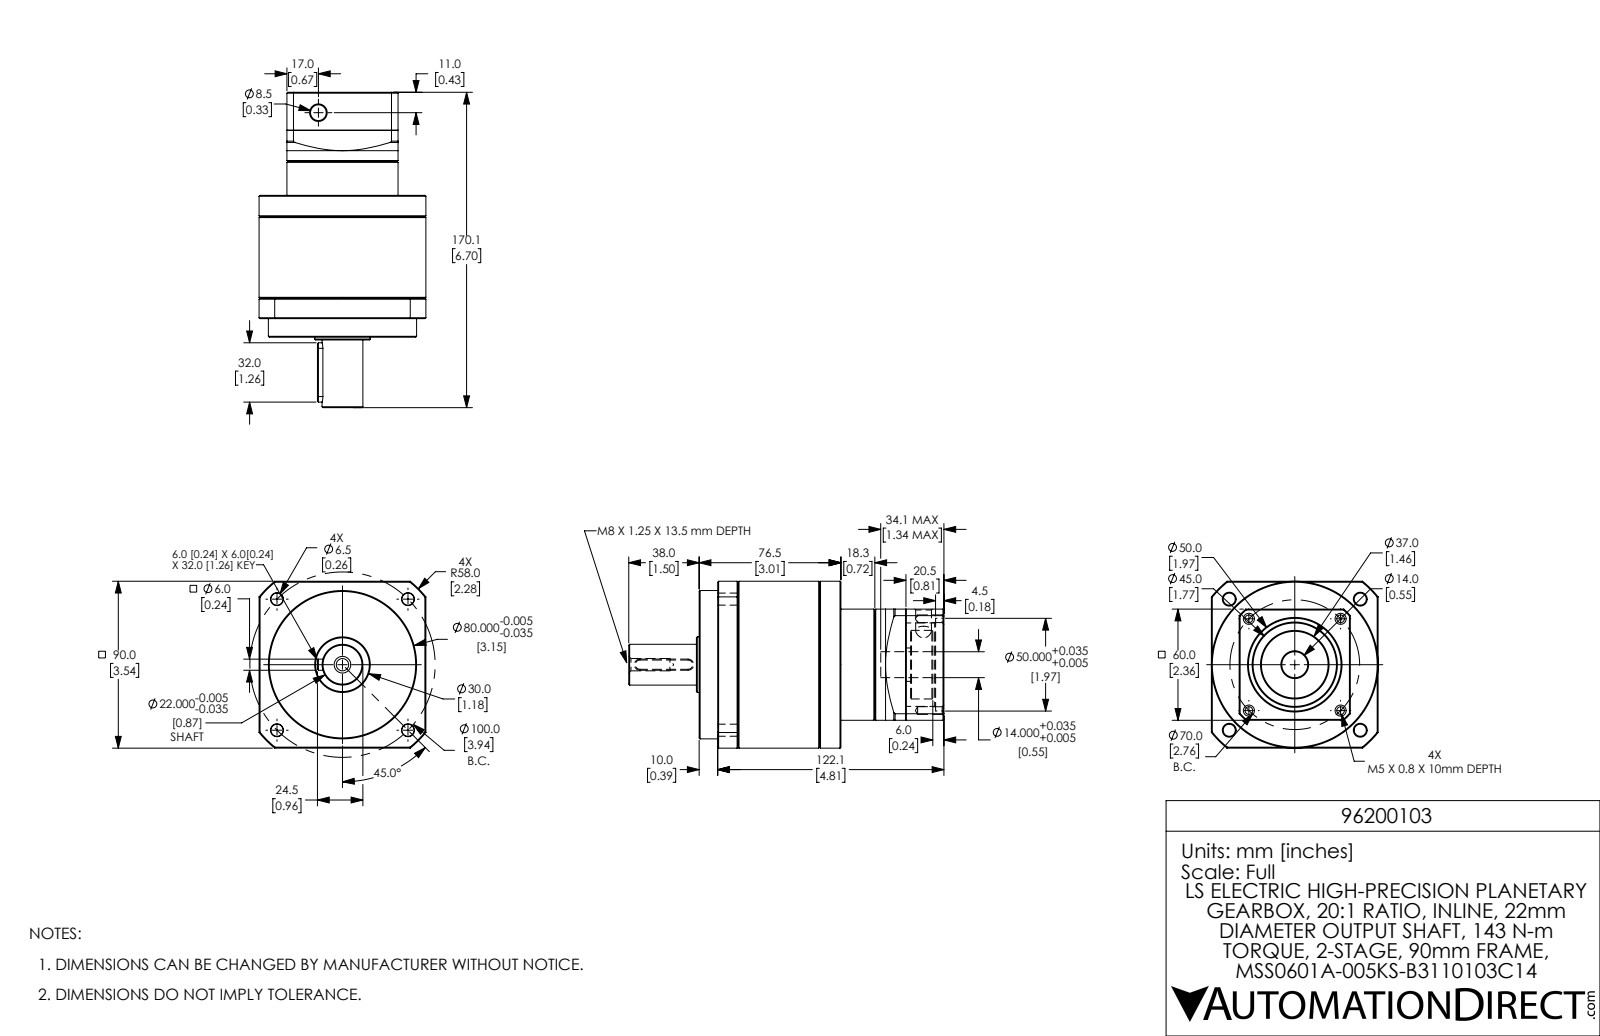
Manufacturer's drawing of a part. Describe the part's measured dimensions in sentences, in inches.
The part is named "MSS0902B-B3110103". Its 3-D file was written by "SolidWorks 2017 (AUTOMOTIVE_DESIGN)". It is 3 solids with 194 faces: 47 planar, 58 cylindrical and 89 other. Overall it measures 6.697 by 3.543 by 3.543 inches. Its volume is 40.07 cubic inches and its surface area 112 square inches. Round holes: 4 of diameter 0.163, 4 of diameter 0.256, 1 of diameter 0.262, 1 of diameter 0.335, 1 of diameter 0.551, 1 of diameter 1.772, 1 of diameter 1.969. Round bosses or shafts: 1 of diameter 3.543, 1 of diameter 3.15, 1 of diameter 2.362, 1 of diameter 1.457, 1 of diameter 1.181, 1 of diameter 0.866, 1 of diameter 0.709. Partial cylindrical surfaces (rounded edges, fillets, slot ends): 2 of radius 0.118, 1 of radius 2.283. The main face-to-face distances are 0.661, 4.394, 3.732, 1.382, 0.72, 3.012, 2.362, 0.591, 2.953, 4. The hole center spacings are 2.403, 0.591, 1.378, 1.949, 1.969, 1.969, 2.403, 2.756.
